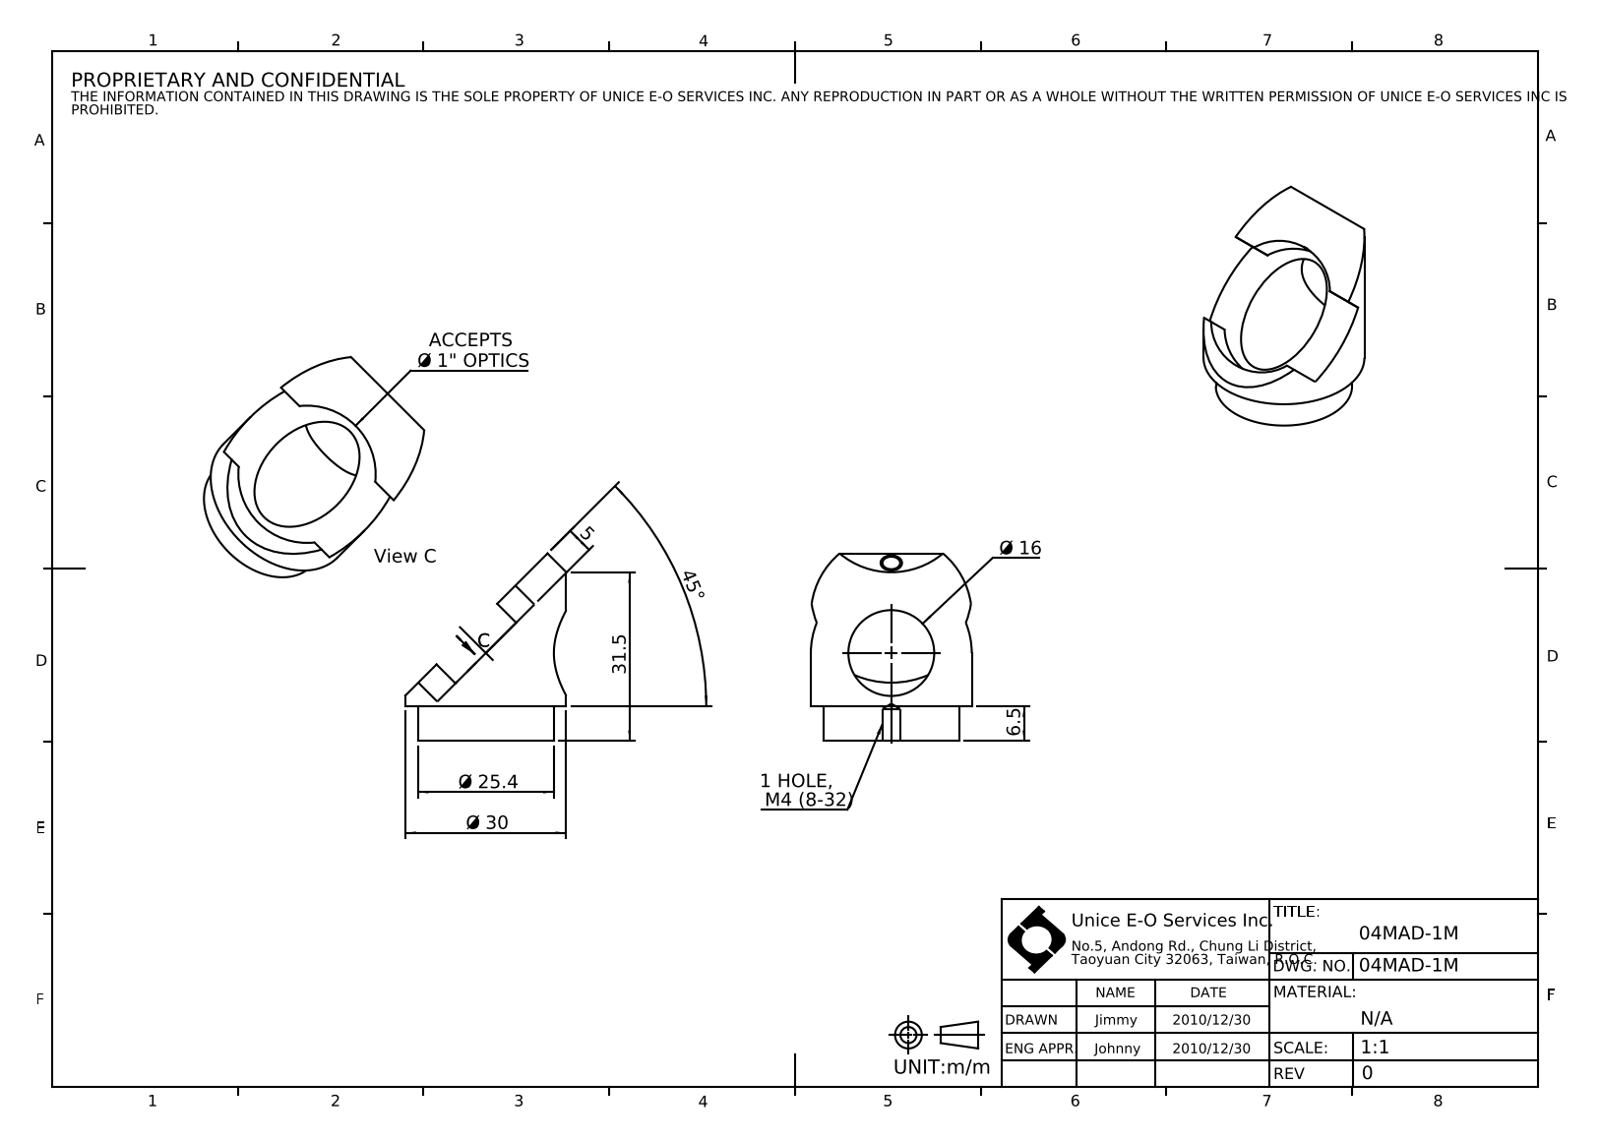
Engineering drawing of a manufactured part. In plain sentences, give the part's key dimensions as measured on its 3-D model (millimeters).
The part is named "04MAD-1M". Its 3-D file was written by "SolidWorks 2016 (CONFIG_CONTROL_DESIGN)". It is 1 solid with 25 faces: 10 planar, 13 cylindrical and 2 other. Overall it measures 35 by 30 by 30 millimeters. Its volume is 9 146 cubic millimeters and its surface area 4 238 square millimeters. Round holes: 1 of diameter 3.3, 1 of diameter 3.45, 1 of diameter 16. Round bosses or shafts: 1 of diameter 30, 1 of diameter 25.4. Partial cylindrical surfaces (rounded edges, fillets, slot ends): 1 of radius 12.8. The main face-to-face distances are 5, 6.5, 13.26, 16, 29.26.
